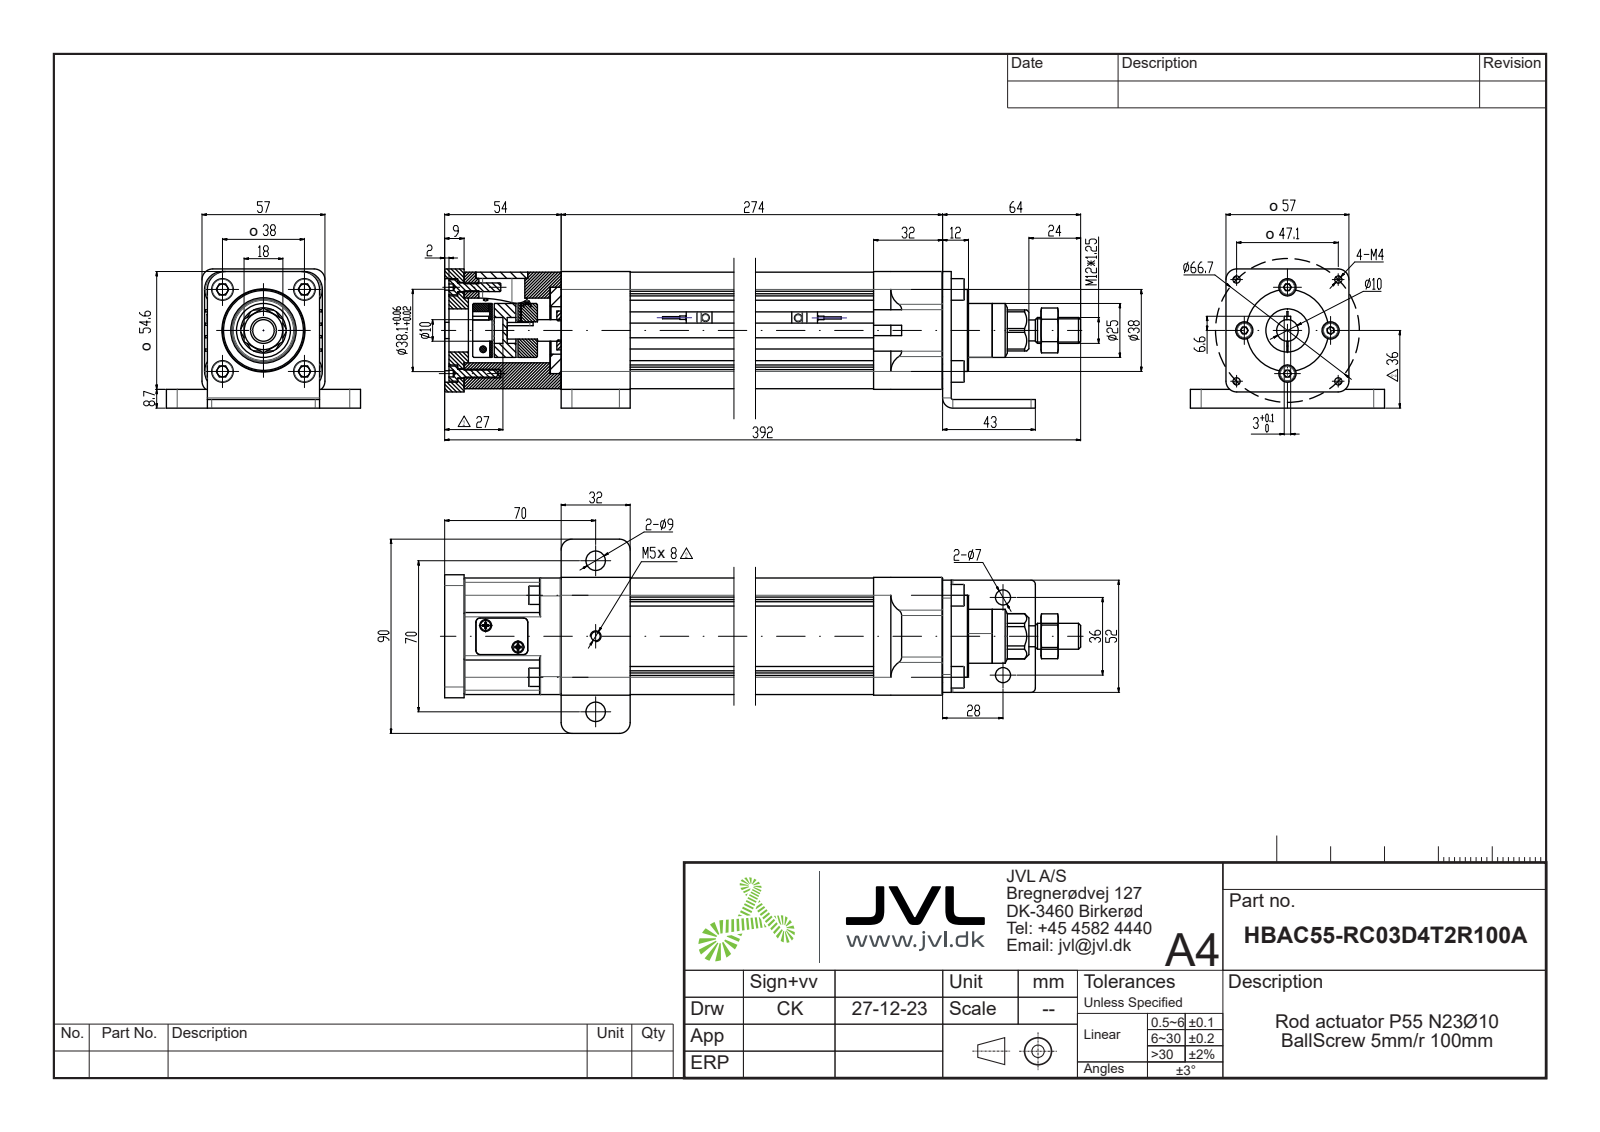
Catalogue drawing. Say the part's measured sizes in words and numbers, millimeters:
The part is named "hex nuts 1-fine pitch-grades ab gb_GB_FASTENER_NUT_SNAB1XY M12X1.25-N_1; socket head cap screw_iso_ISO 4762 M4 x 20 - 20N_1; HBAC55-RC0D4T2R100A; AOE-40-1-2-100 (+8 more)". Its 3-D file was written by "SolidWorks 2023 (AUTOMOTIVE_DESIGN)". It is 69 solids with 2621 faces: 938 planar, 781 cylindrical and 902 other. Overall it measures 394 by 90 by 64.5 millimeters. Its volume is 747 182 cubic millimeters and its surface area 320 104 square millimeters. Round holes: 14 of diameter 3.3, 6 of diameter 4.3, 5 of diameter 8, 4 of diameter 4.5, 4 of diameter 5, 4 of diameter 6.4, 4 of diameter 6.5, 4 of diameter 6.6, 4 of diameter 9.5, 2 of diameter 2.05, 2 of diameter 2.5, 2 of diameter 2.9. Round bosses or shafts: 10 of diameter 7, 10 of diameter 4, 6 of diameter 8.5, 4 of diameter 10, 4 of diameter 9, 4 of diameter 6, 4 of diameter 3, 2 of diameter 5.5. Partial cylindrical surfaces (rounded edges, fillets, slot ends): 40 of radius 0.2, 20 of radius 0.5, 18 of radius 2, 13 of radius 7.5, 12 of radius 1, 10 of radius 5, 10 of radius 8.3, 8 of radius 3. The main face-to-face distances are 54, 5, 54.3, 9, 63, 4, 32, 242, 45, 4.5. The hole center spacings are 14.26, 19.03, 23.84, 31.27, 33.29, 36.97, 42.81, 43.38.
